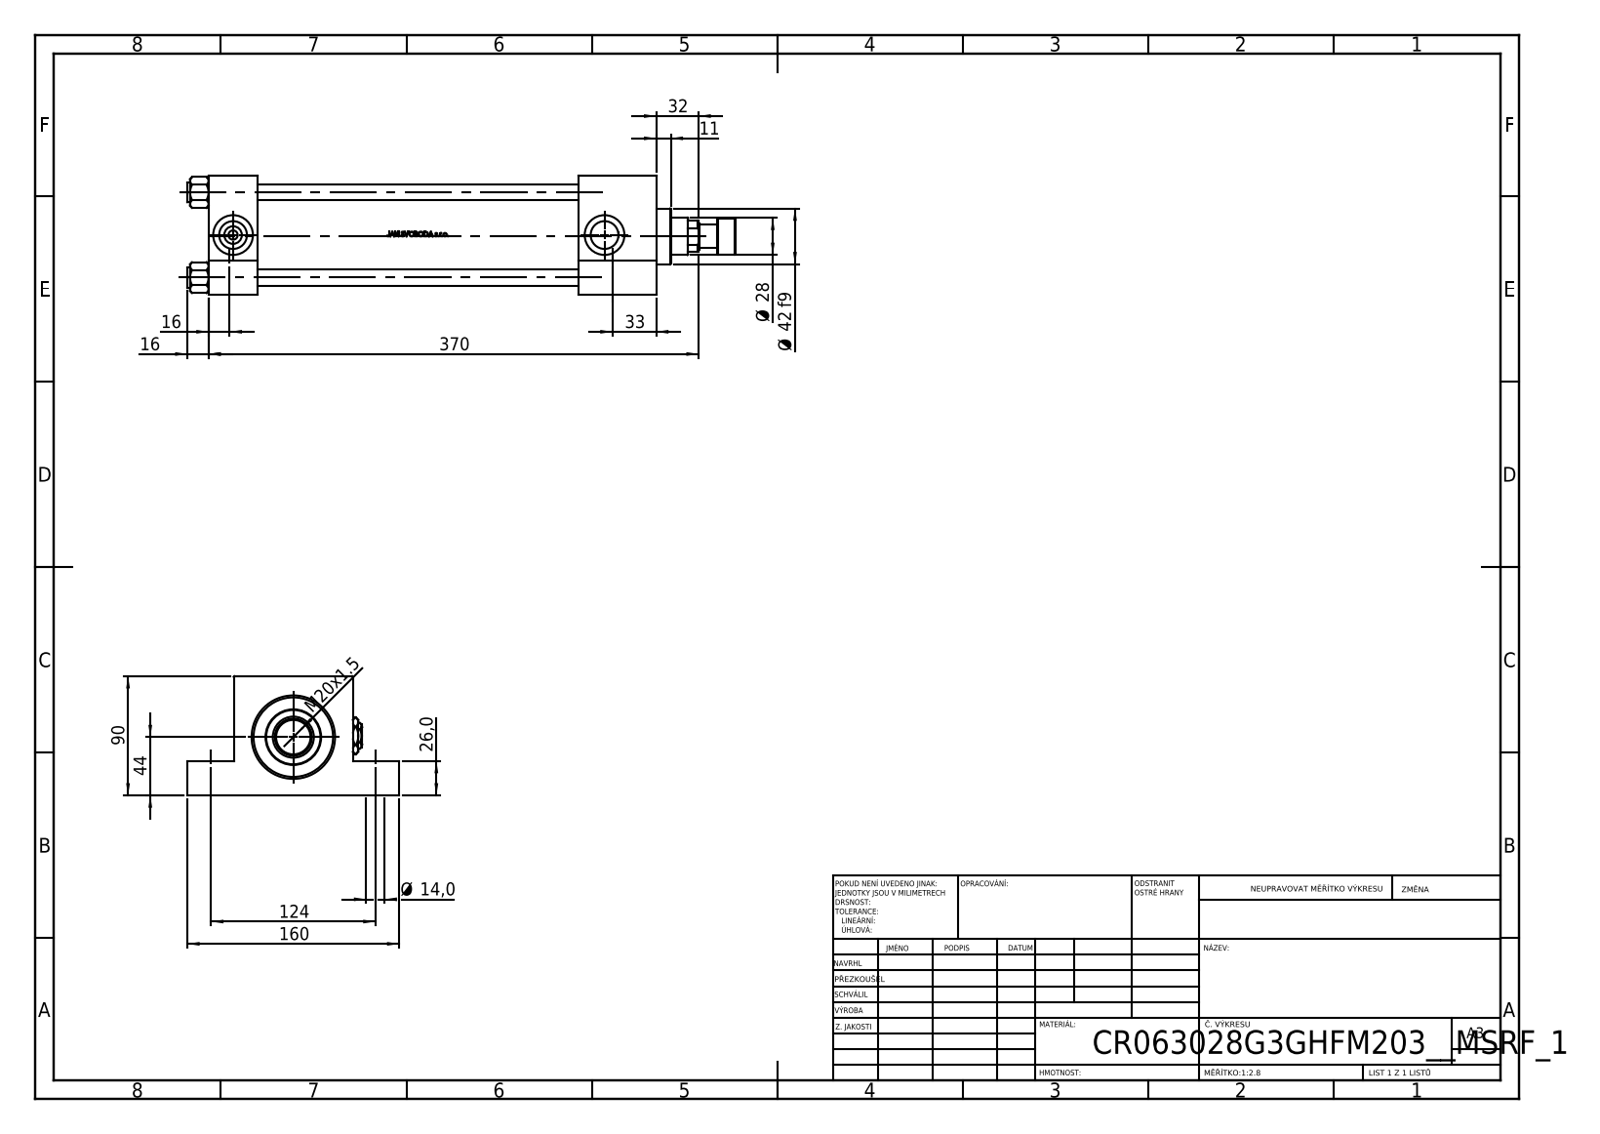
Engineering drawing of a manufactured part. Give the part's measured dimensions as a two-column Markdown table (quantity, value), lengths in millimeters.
| quantity | value |
| --- | --- |
| part name | V215CR_G_TYCINKA; V215CR_VCP_G; V215CR_G_Body; NUT_M5_G (+3 more) |
| STEP written by | SolidWorks 2019 (CONFIG_CONTROL_DESIGN) |
| units | millimeters |
| bodies | 14 solids, 1198 faces (482 planar, 136 cylindrical, 580 other) |
| overall size | 414 × 160 × 90 |
| volume | 1 431 000 mm³ |
| surface area | 327 164 mm² |
| round holes (diameter × count) | 12 × 4, 14 × 4, 7 × 2, 20.96 × 2, 30 × 2, 18.5 × 1, 28 × 1, 31 × 1, 50 × 1, 60 × 1, 63 × 1 |
| round bosses / shafts (diameter × count) | 15 × 4, 69 × 1, 42 × 1, 27 × 1, 18 × 1 |
| main face-to-face distances | 90, 37, 301, 338, 59, 279, 242, 64, 26, 35 |
| hole center spacings | 64.3, 44.77, 46.18, 90.93, 124, 289, 314.48, 280.5 |
